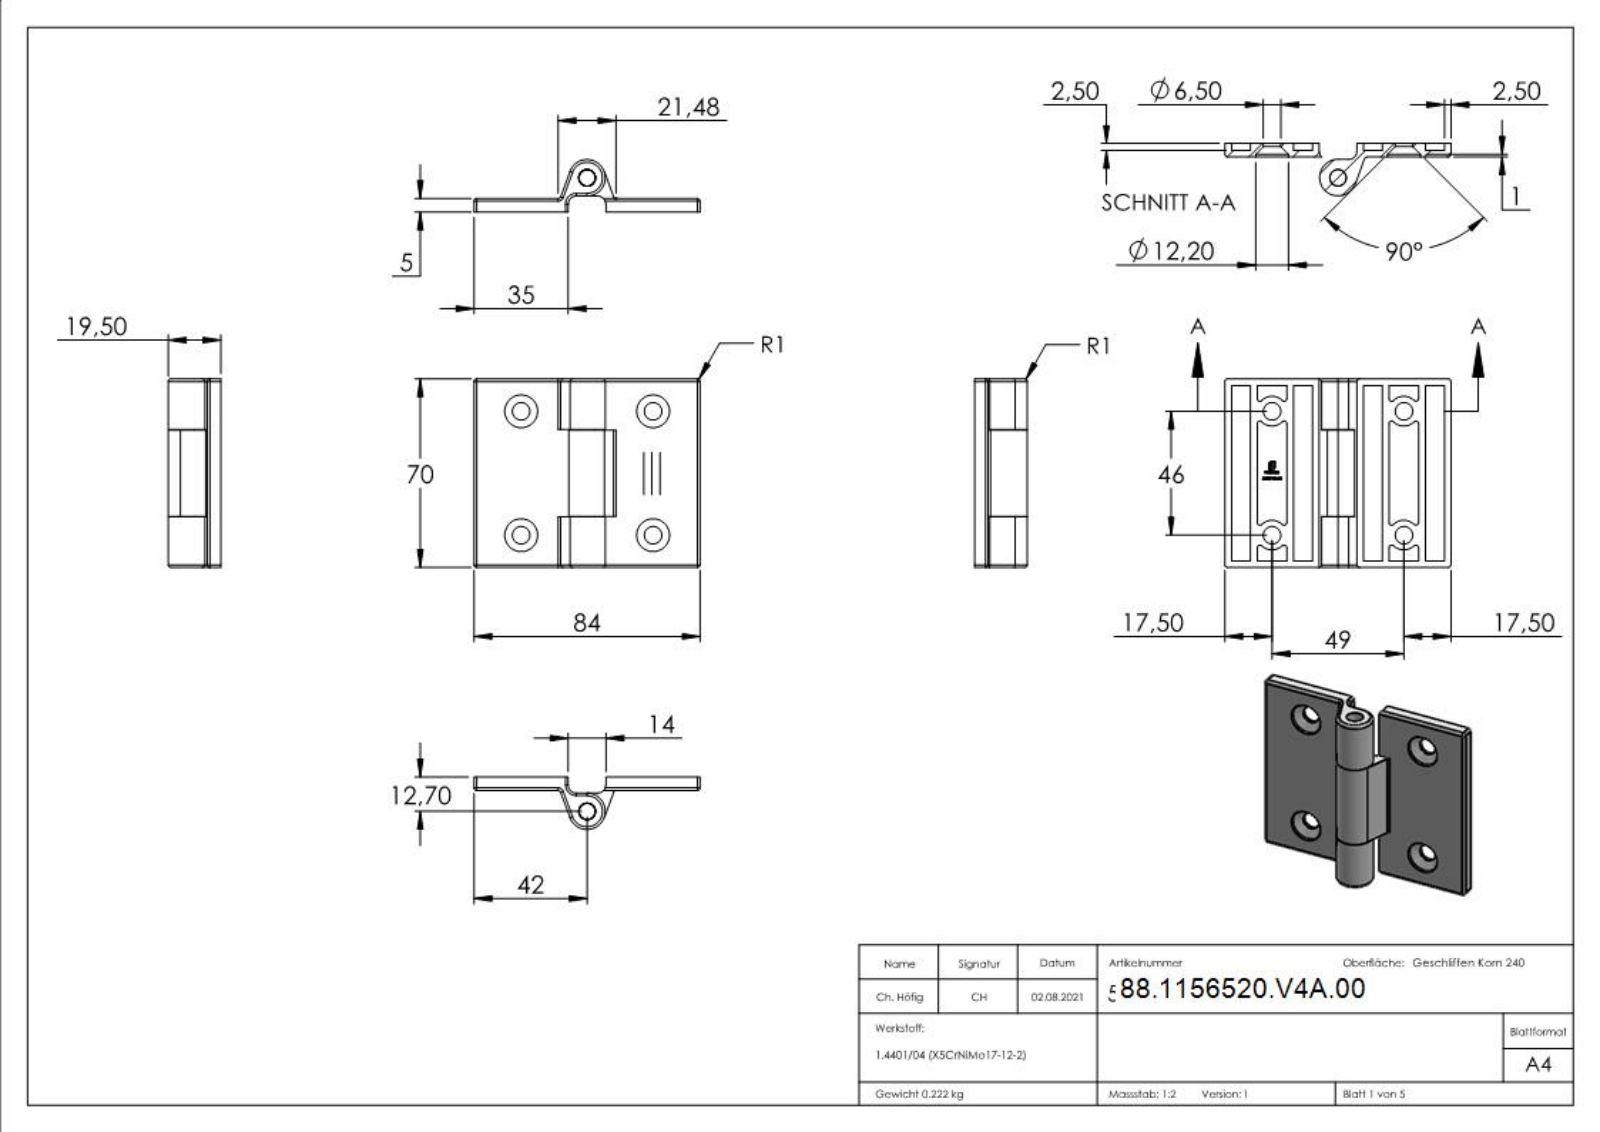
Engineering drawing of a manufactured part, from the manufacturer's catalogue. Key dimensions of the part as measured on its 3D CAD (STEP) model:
Part name (STEP PRODUCT): 5652X-V4A-XX Teil1; 56520-V4A-00; 5652X-V4A-XX Teil1_56520-V4A-00 Teil2; 5652X-V4A-XX Teil1_56520-V4A-00 Teil1 (+1 more)
STEP written by: SolidWorks 2018 (CONFIG_CONTROL_DESIGN)
Units: millimetres
Bodies: 3 solids, 752 faces (472 planar, 140 cylindrical, 140 other)
Overall size (bounding box): 84 × 70 × 19.5
Volume: 27 767 mm³ · Surface area: 20 995 mm²
Round holes (diameter × count): ⌀6.5 ×4, ⌀12.2 ×4
Round bosses / shafts (diameter × count): ⌀13.6 ×1, ⌀6.2 ×1, ⌀6 ×1
Partial cylindrical surfaces — rounded edges, fillets, slot ends (radius × count): R1 ×32, R5.5 ×4, R3 ×2
Main face-to-face distances: 2.5, 5, 49, 23, 9.5, 32.5, 25.5, 7, 16.5, 51.5
Hole centre spacings: 46, 49, 67.21
